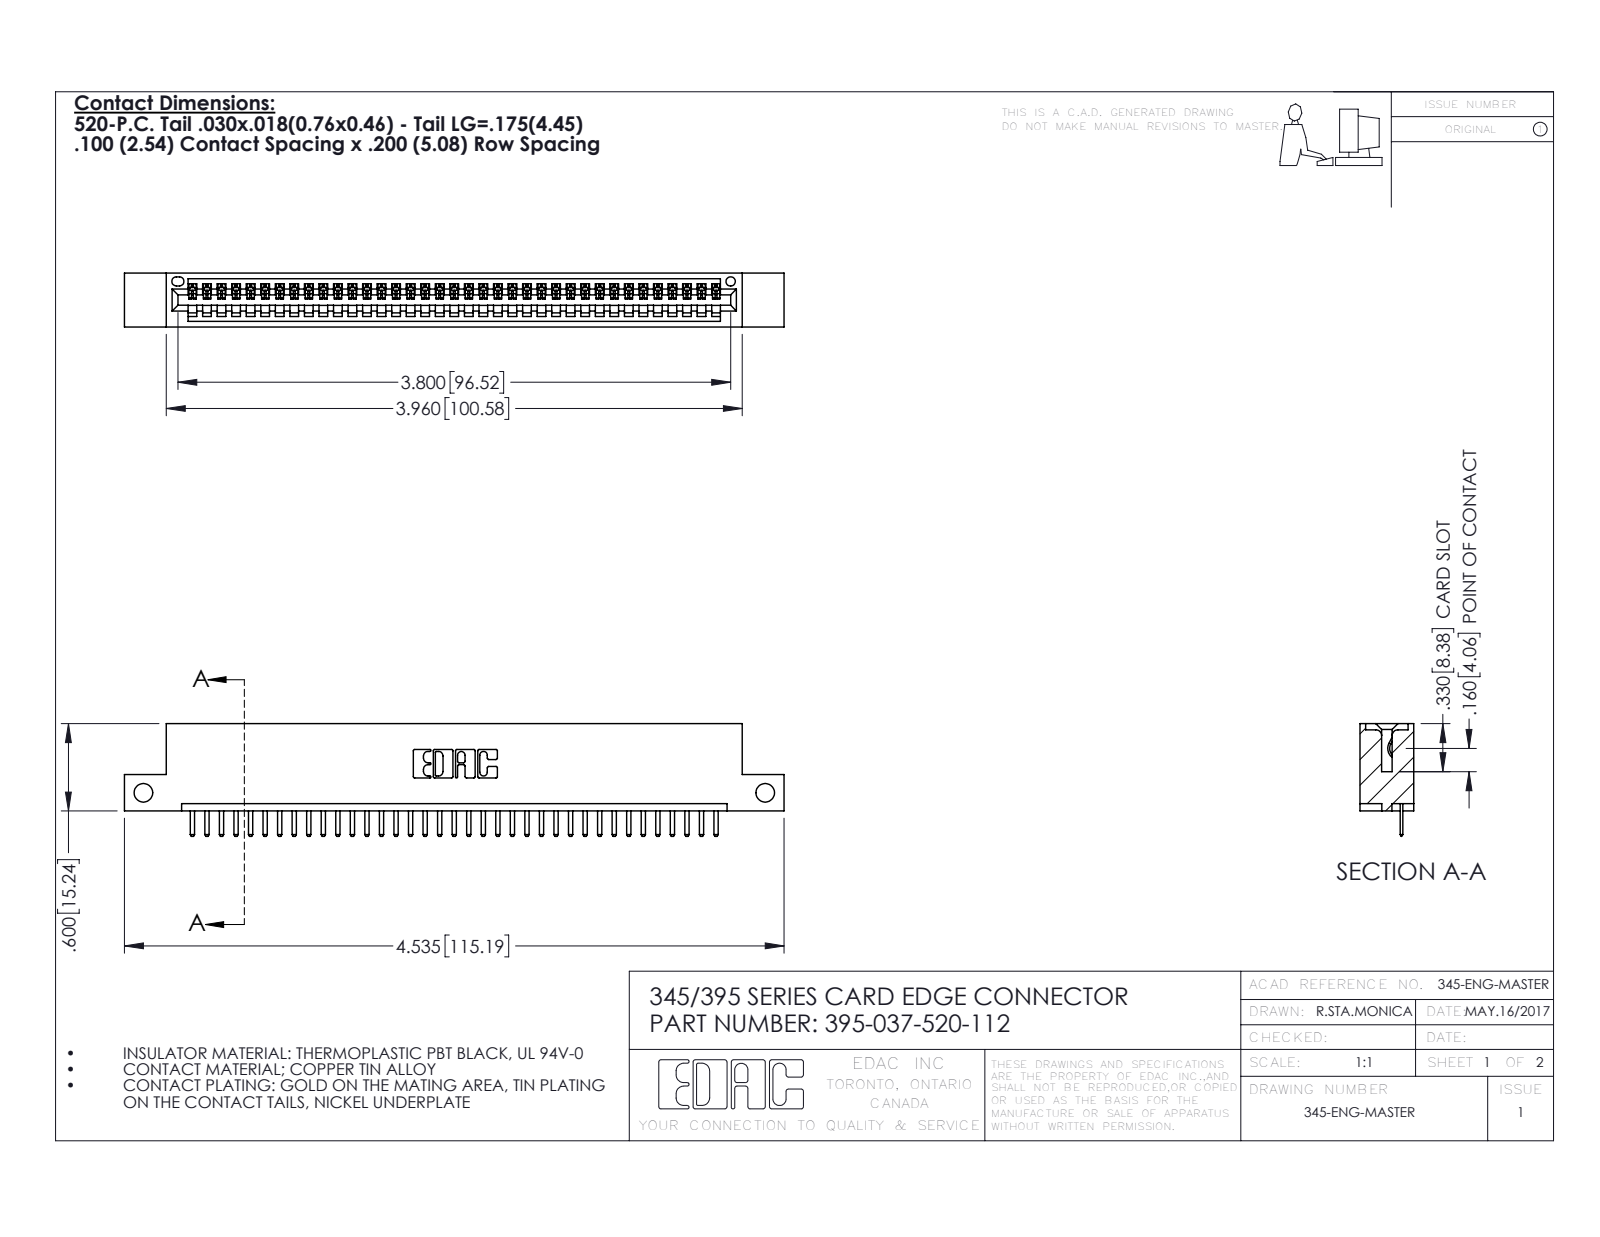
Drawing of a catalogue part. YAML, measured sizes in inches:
part_name: "345 Part_Flush Mounting Lugs - Side Mount; 395-037-520-112; 345-292-001_345-293-120"
step_written_by: "SolidWorks 2016 (CONFIG_CONTROL_DESIGN)"
units: inches
bodies: {solids: 38, faces: 2420, planar: 1634, cylindrical: 786, other: 0}
overall_size: [4.535, 0.775, 0.37]
volume: 0.653
surface_area: 21.19
round_holes:
  - {diameter: 0.128, count: 2}
  - {diameter: 0.064, count: 1}
partial_cylinders:
  - {radius: 0.01, count: 76}
  - {radius: 0.006, count: 74}
  - {radius: 0.01, count: 22}
  - {radius: 0.007, count: 6}
  - {radius: 0.031, count: 6}
  - {radius: 0.026, count: 3}
  - {radius: 0.031, count: 2}
  - {radius: 0.04, count: 2}
face_to_face_distances: [0.298, 0.072, 0.37, 0.2, 0.098, 0.272, 0.025, 0.225, 0.072, 0.149]
hole_center_spacings: [4.275]
